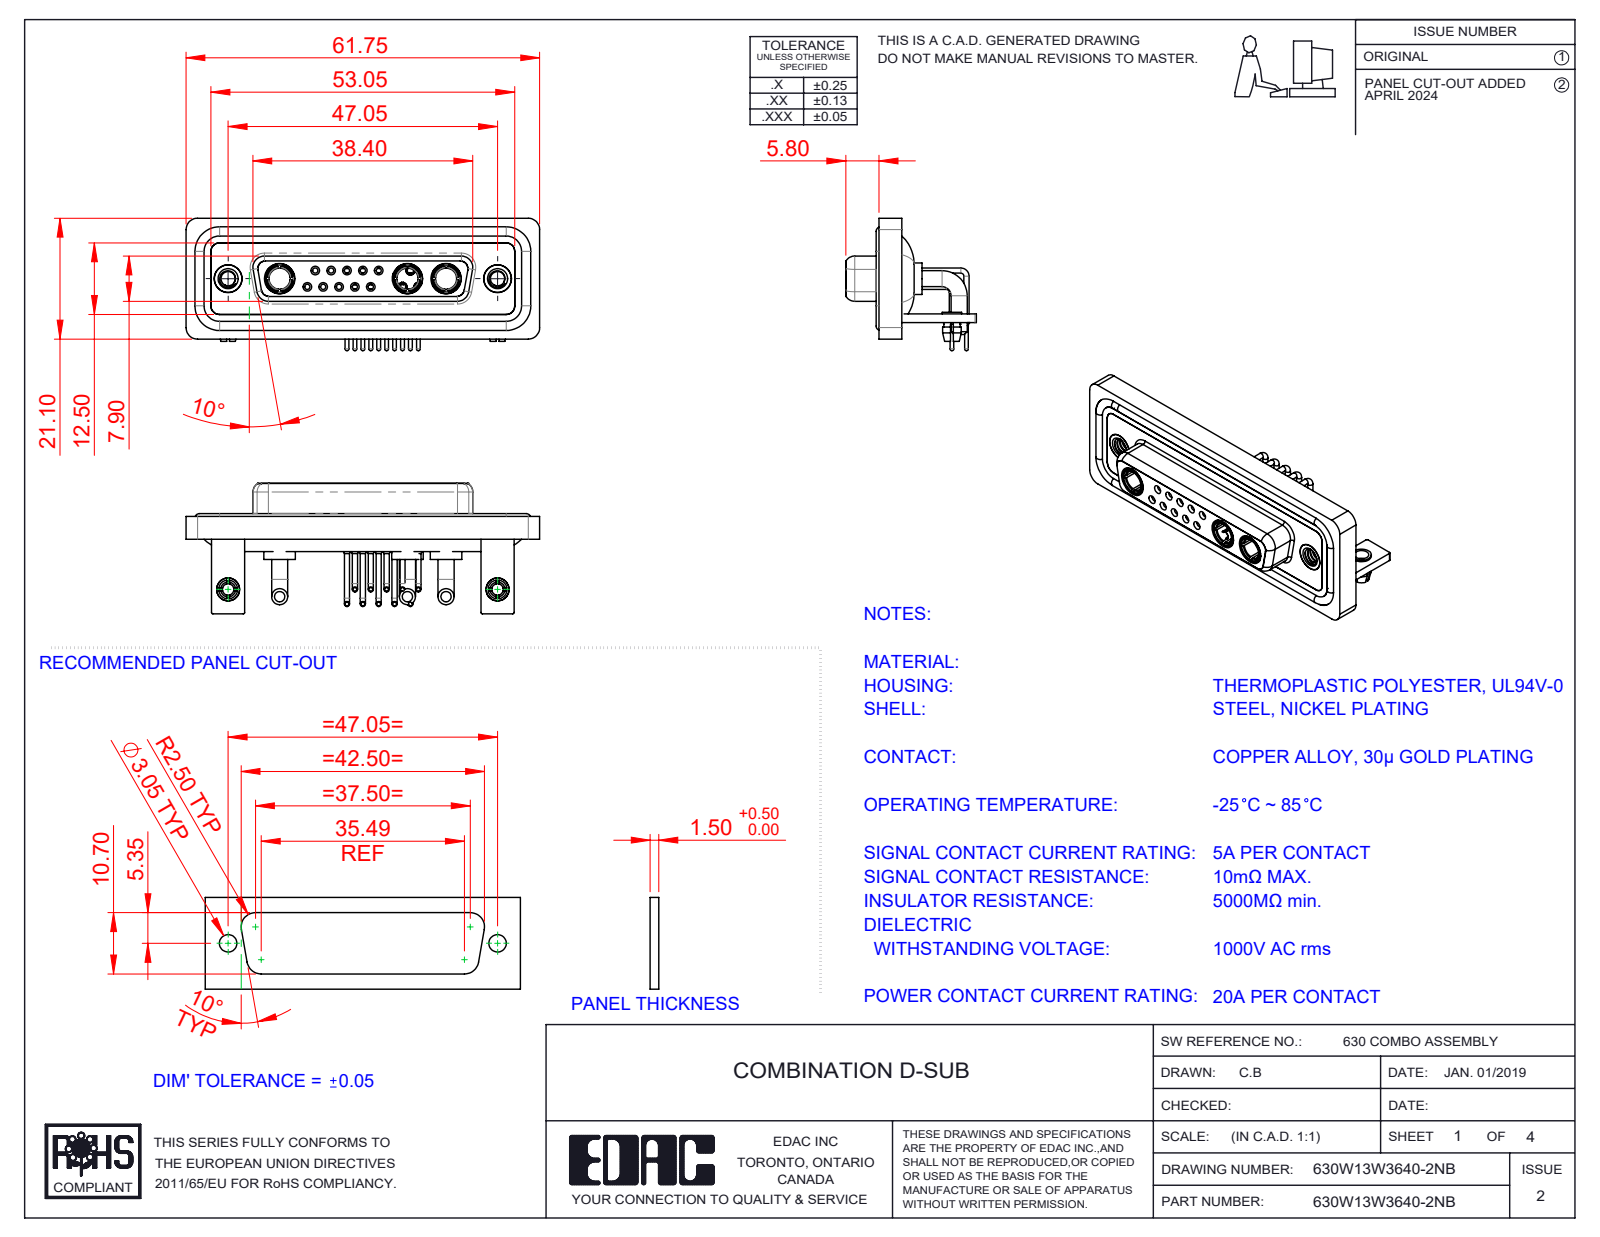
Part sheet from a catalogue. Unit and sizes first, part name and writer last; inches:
Units: inches
Overall size (bounding box): 2.431 × 0.91 × 0.898
Round holes (diameter × count): ⌀0.079 ×12, ⌀0.035 ×10, ⌀0.043 ×10, ⌀0.059 ×10, ⌀0.063 ×5, ⌀0.067 ×5, ⌀0.191 ×5, ⌀0.098 ×4, ⌀0.146 ×3, ⌀0.209 ×3, ⌀0.126 ×2, ⌀0.157 ×2
Round bosses / shafts (diameter × count): ⌀0.035 ×15, ⌀0.063 ×12, ⌀0.026 ×10, ⌀0.11 ×6, ⌀0.079 ×5, ⌀0.059 ×5, ⌀0.217 ×3, ⌀0.205 ×3
Partial cylindrical surfaces — rounded edges, fillets, slot ends (radius × count): R0.079 ×19, R0.059 ×18, R0.01 ×16, R0.053 ×8, R0.063 ×8, R0.02 ×5, R0.024 ×4, R0.026 ×4
Main face-to-face distances: 0.016, 0.071, 0.114, 0.059, 0.146, 0.161, 0.043, 0.055, 0.063, 0.122
Hole centre spacings: 0.124, 0.109, 0.218, 0.198, 0.327, 0.198, 0.295, 0.436
Volume: 0.541 in³ · Surface area: 23.63 in²
Bodies: 27 solids, 1284 faces (410 planar, 547 cylindrical, 327 other)
Part name (STEP PRODUCT): Power Socket_20A RA; 630Combo Housing_13W3; 630Combo Contact Row 1_50 Contacts; 630Combo Board Lock_50 Contacts (+7 more)
STEP written by: SolidWorks 2023 (CONFIG_CONTROL_DESIGN)
